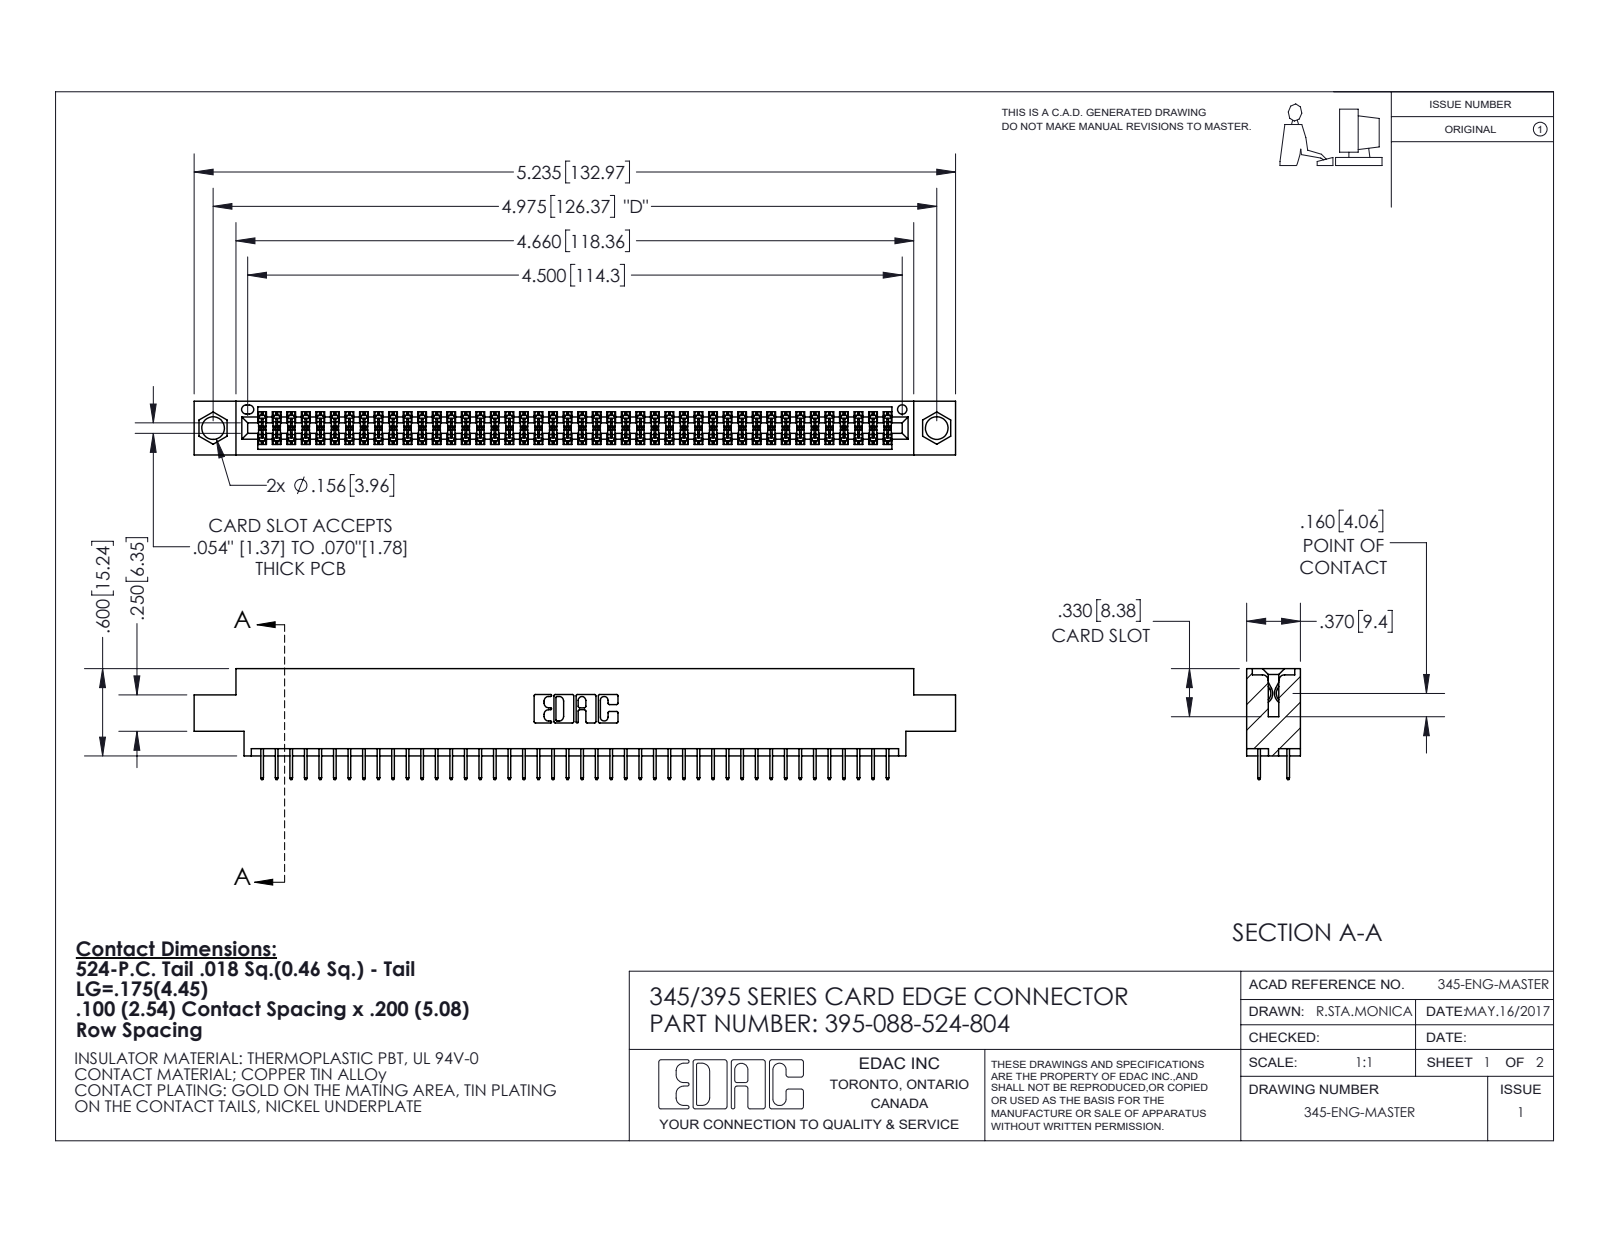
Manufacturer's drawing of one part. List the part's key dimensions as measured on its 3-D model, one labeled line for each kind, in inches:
Part name (STEP PRODUCT): 395-088-524-804; 345 Part_0.170 Offset - 0.156 Dia-TI; 345-292-001_345-293-124
STEP written by: SolidWorks 2020 (CONFIG_CONTROL_DESIGN)
Units: inches
Bodies: 89 solids, 4896 faces (3530 planar, 1366 cylindrical, 0 other)
Overall size (bounding box): 5.235 × 0.762 × 0.37
Volume: 0.768 in³ · Surface area: 28.34 in²
Round holes (diameter × count): ⌀0.156 ×2, ⌀0.064 ×1
Partial cylindrical surfaces — rounded edges, fillets, slot ends (radius × count): R0.006 ×132, R0.01 ×22, R0.007 ×6, R0.031 ×6, R0.026 ×3, R0.014 ×2, R0.019 ×2, R0.022 ×2
Main face-to-face distances: 0.072, 0.298, 0.37, 0.2, 0.098, 0.272, 0.025, 0.225, 0.175, 0.072
Hole centre spacings: 0.27, 4.739, 4.975
